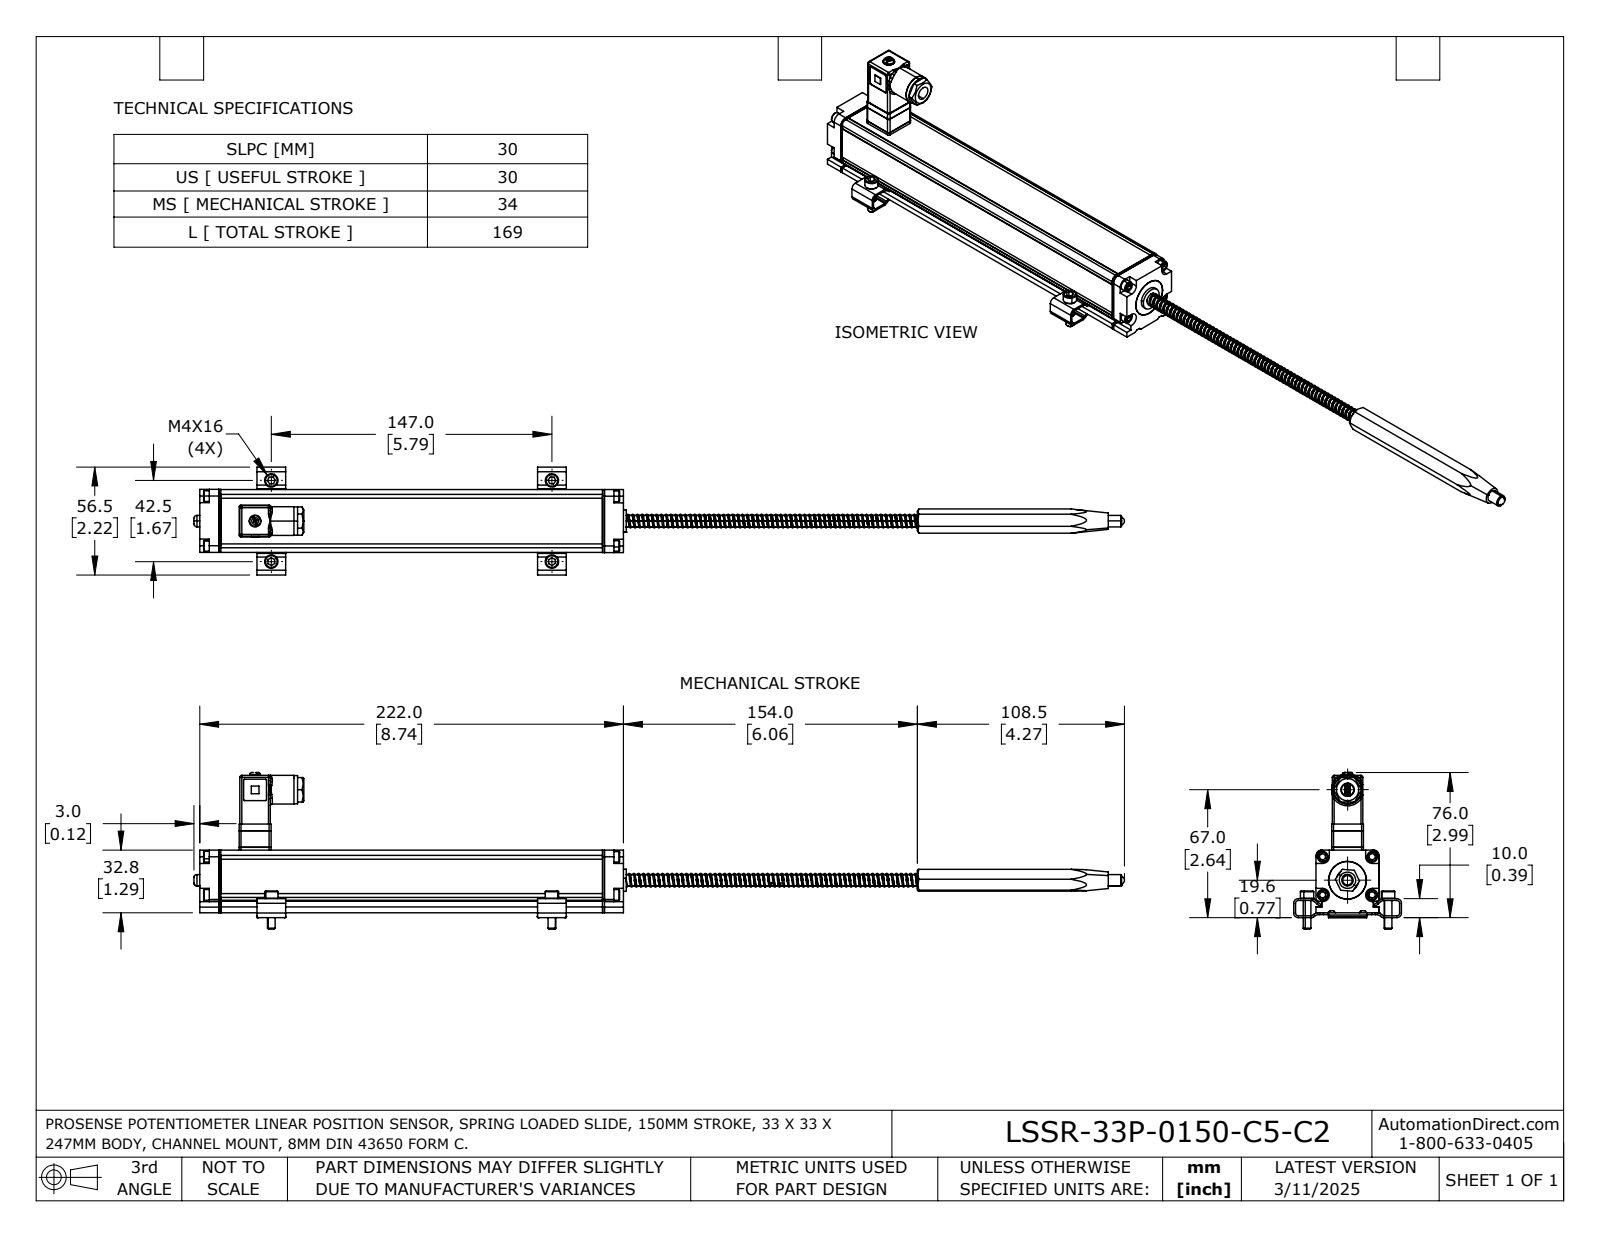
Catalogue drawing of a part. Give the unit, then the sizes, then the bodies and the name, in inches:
Units: inches
Overall size (bounding box): 19.192 × 3.228 × 2.224
Round holes (diameter × count): ⌀0.114 ×16, ⌀0.138 ×8, ⌀0.142 ×8, ⌀0.055 ×4, ⌀0.091 ×4, ⌀0.197 ×4, ⌀0.709 ×4, ⌀0.244 ×3, ⌀0.079 ×2, ⌀0.11 ×2, ⌀0.154 ×2, ⌀0.268 ×2
Round bosses / shafts (diameter × count): ⌀0.079 ×16, ⌀0.22 ×9, ⌀0.118 ×8, ⌀0.276 ×4, ⌀0.157 ×4, ⌀0.776 ×2, ⌀0.503 ×2, ⌀0.177 ×2
Partial cylindrical surfaces — rounded edges, fillets, slot ends (radius × count): R0.039 ×32, R0.079 ×20, R0.051 ×8, R0.059 ×8, R0.089 ×8, R0.118 ×8, R0.138 ×8, R0.02 ×6
Main face-to-face distances: 0.039, 1.291, 1.295, 0.118, 0.433, 7.913, 0.079, 0.394, 0.354, 8.346
Hole centre spacings: 0.343, 0.546, 0.583, 0.786, 1.063, 0.204, 1.037, 1.067
Volume: 16.56 in³ · Surface area: 146.6 in²
Bodies: 38 solids, 1413 faces (679 planar, 573 cylindrical, 161 other)
Part name (STEP PRODUCT): LSSR-33P-0150-B5-C2
STEP written by: SolidWorks 2024 (AUTOMOTIVE_DESIGN)
